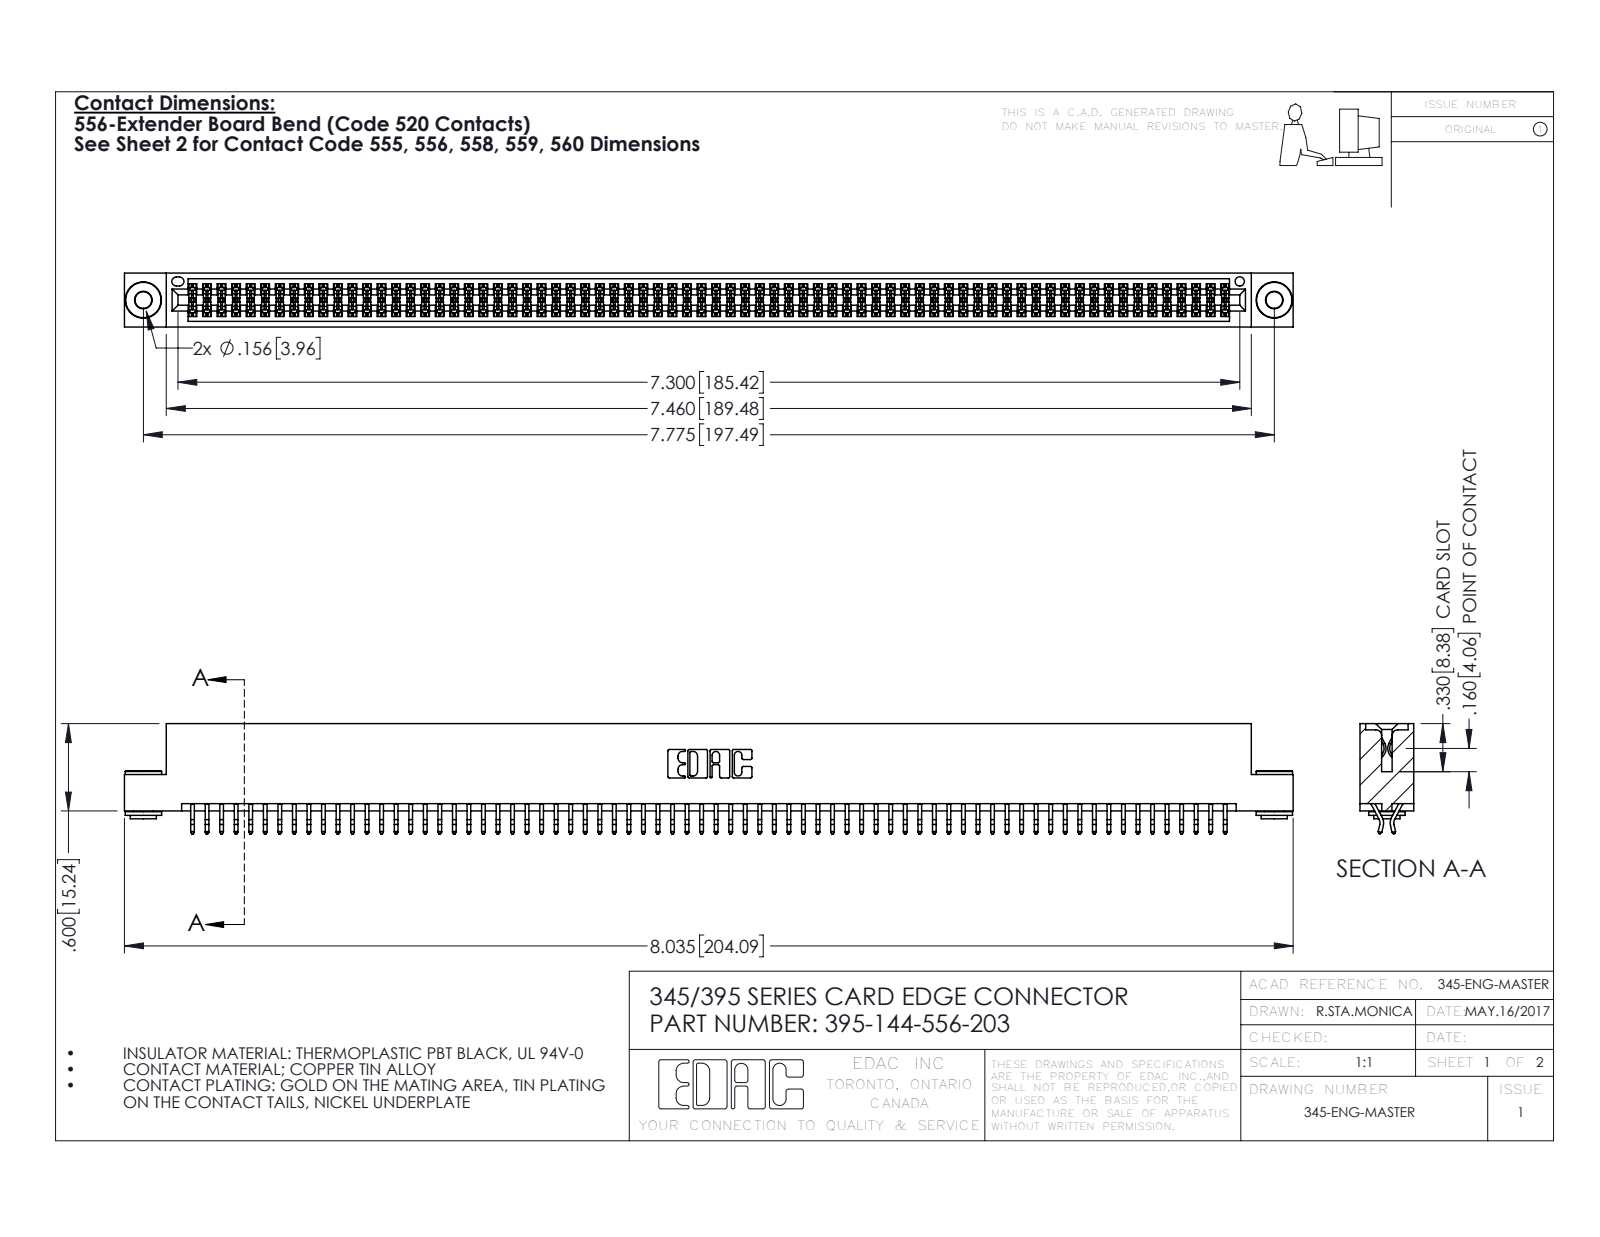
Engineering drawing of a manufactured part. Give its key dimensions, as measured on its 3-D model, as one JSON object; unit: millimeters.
{"part_name": "345-292-001_556 Tail; 395-144-556-203; 345 Part_Flush Mounting Lugs - 0.156 Dia-TH; 345-250-002_345-250-002-102", "step_written_by": "SolidWorks 2016 (CONFIG_CONTROL_DESIGN)", "units": "millimeters", "bodies": {"solids": 147, "faces": 8228, "planar": 5418, "cylindrical": 2802, "other": 8}, "overall_size": [204.1, 19.2, 9.4], "volume_mm3": 20120, "surface_area_mm2": 30400, "round_holes": [[2.9, 2], [4, 2], [1.6, 1]], "round_bosses_or_shafts": [[6.4, 2], [4.6, 2], [3.5, 2]], "partial_cylinders_radius": [[0.2, 216], [0.3, 22], [0.2, 6], [0.8, 6], [0.7, 3], [0.3, 2], [0.4, 2], [0.5, 2]], "face_to_face_distances": [1.8, 7.6, 9.4, 5.1, 0.6, 2.5, 6.9, 5.7, 4.4, 3.8], "hole_center_spacings": [6.9, 191.5, 197.5]}
